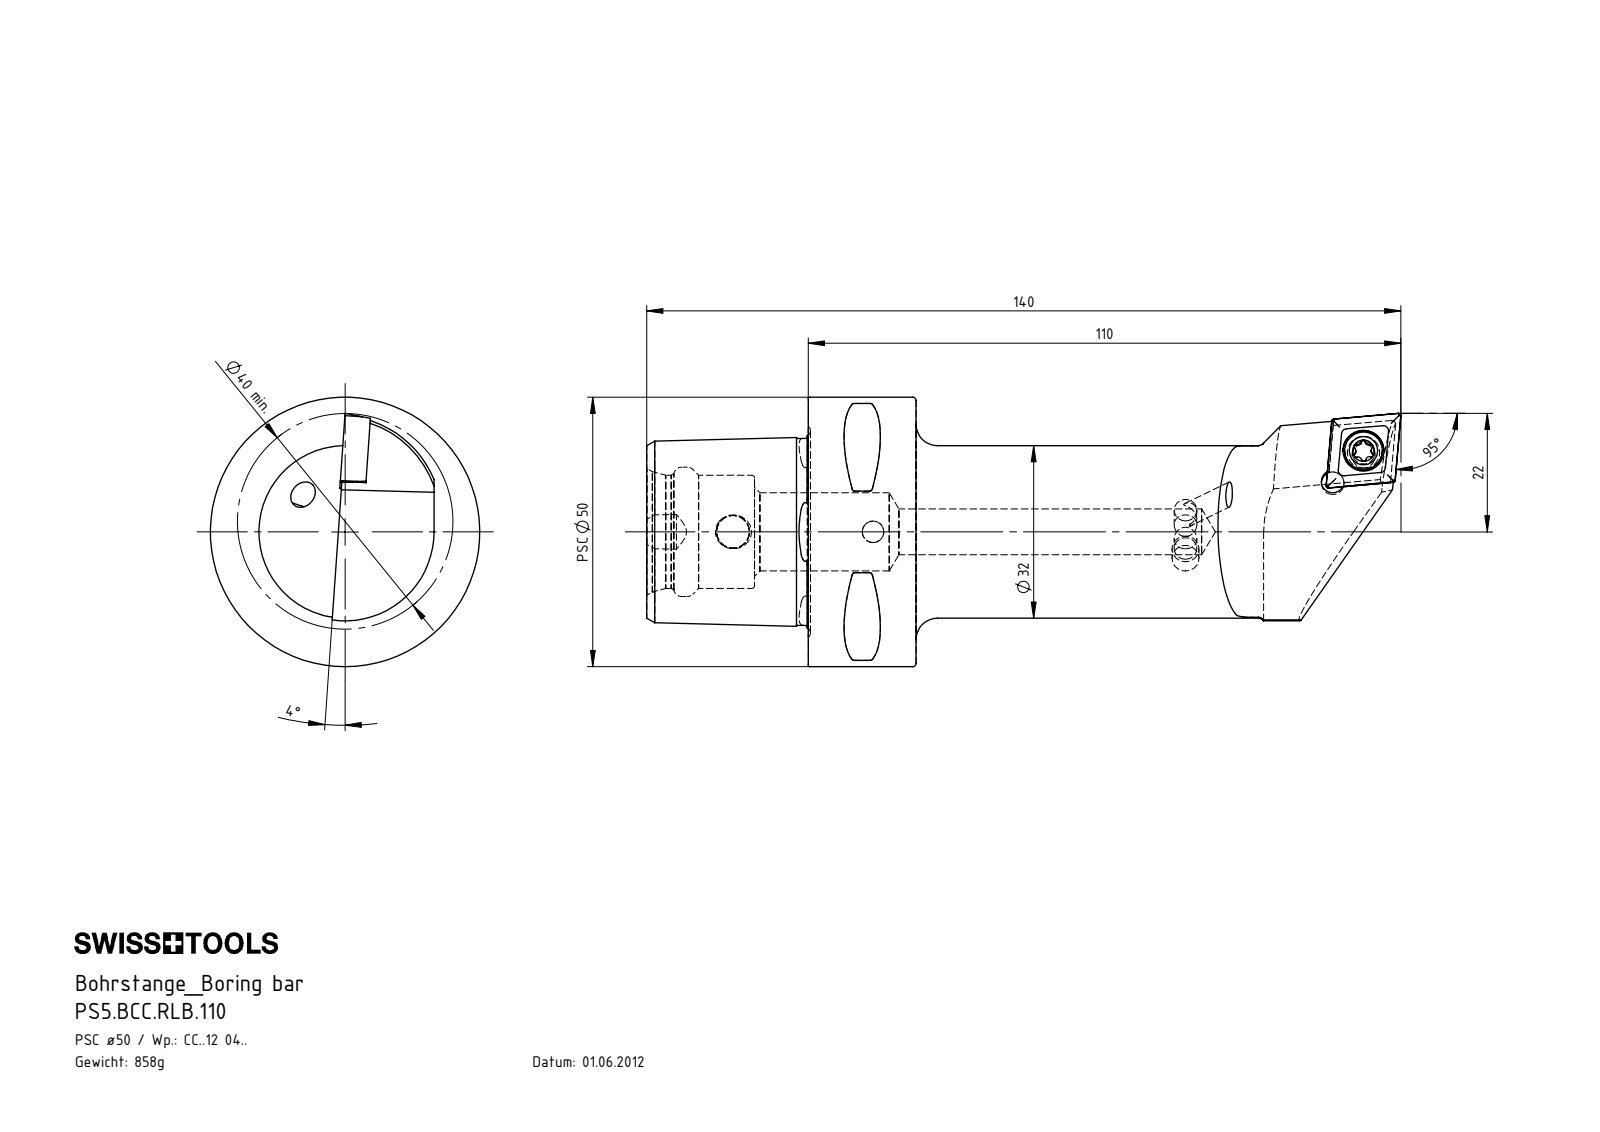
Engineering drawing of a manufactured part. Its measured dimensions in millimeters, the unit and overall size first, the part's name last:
Units: millimetres
Overall size (bounding box): 140 × 50 × 50
Round holes (diameter × count): ⌀4.2 ×4, ⌀4 ×2, ⌀5.5 ×1, ⌀6.1 ×1, ⌀7.6 ×1, ⌀8.5 ×1, ⌀14.5 ×1, ⌀21 ×1, ⌀24 ×1
Round bosses / shafts (diameter × count): ⌀5 ×2, ⌀50 ×1, ⌀32 ×1, ⌀7 ×1
Partial cylindrical surfaces — rounded edges, fillets, slot ends (radius × count): R0.5 ×8, R0.39 ×6, R0.69 ×3, R0.69 ×3, R3 ×1, R4 ×1, R16.5 ×1, R19 ×1
Main face-to-face distances: 20, 30, 50, 4.45, 19.18, 44.4, 10, 29.8, 9.8, 20.2
Hole centre spacings: 8.01, 8.09, 26
Volume: 109 348 mm³ · Surface area: 23 913 mm²
Bodies: 5 solids, 279 faces (49 planar, 73 cylindrical, 157 other)
Part name (STEP PRODUCT): CCMT120404; WCC-ER2.001.010_A; PS5.BCC.RLB.110; KVT_MB_600_050 (+1 more)
STEP written by: SolidWorks 2017 (AUTOMOTIVE_DESIGN)
